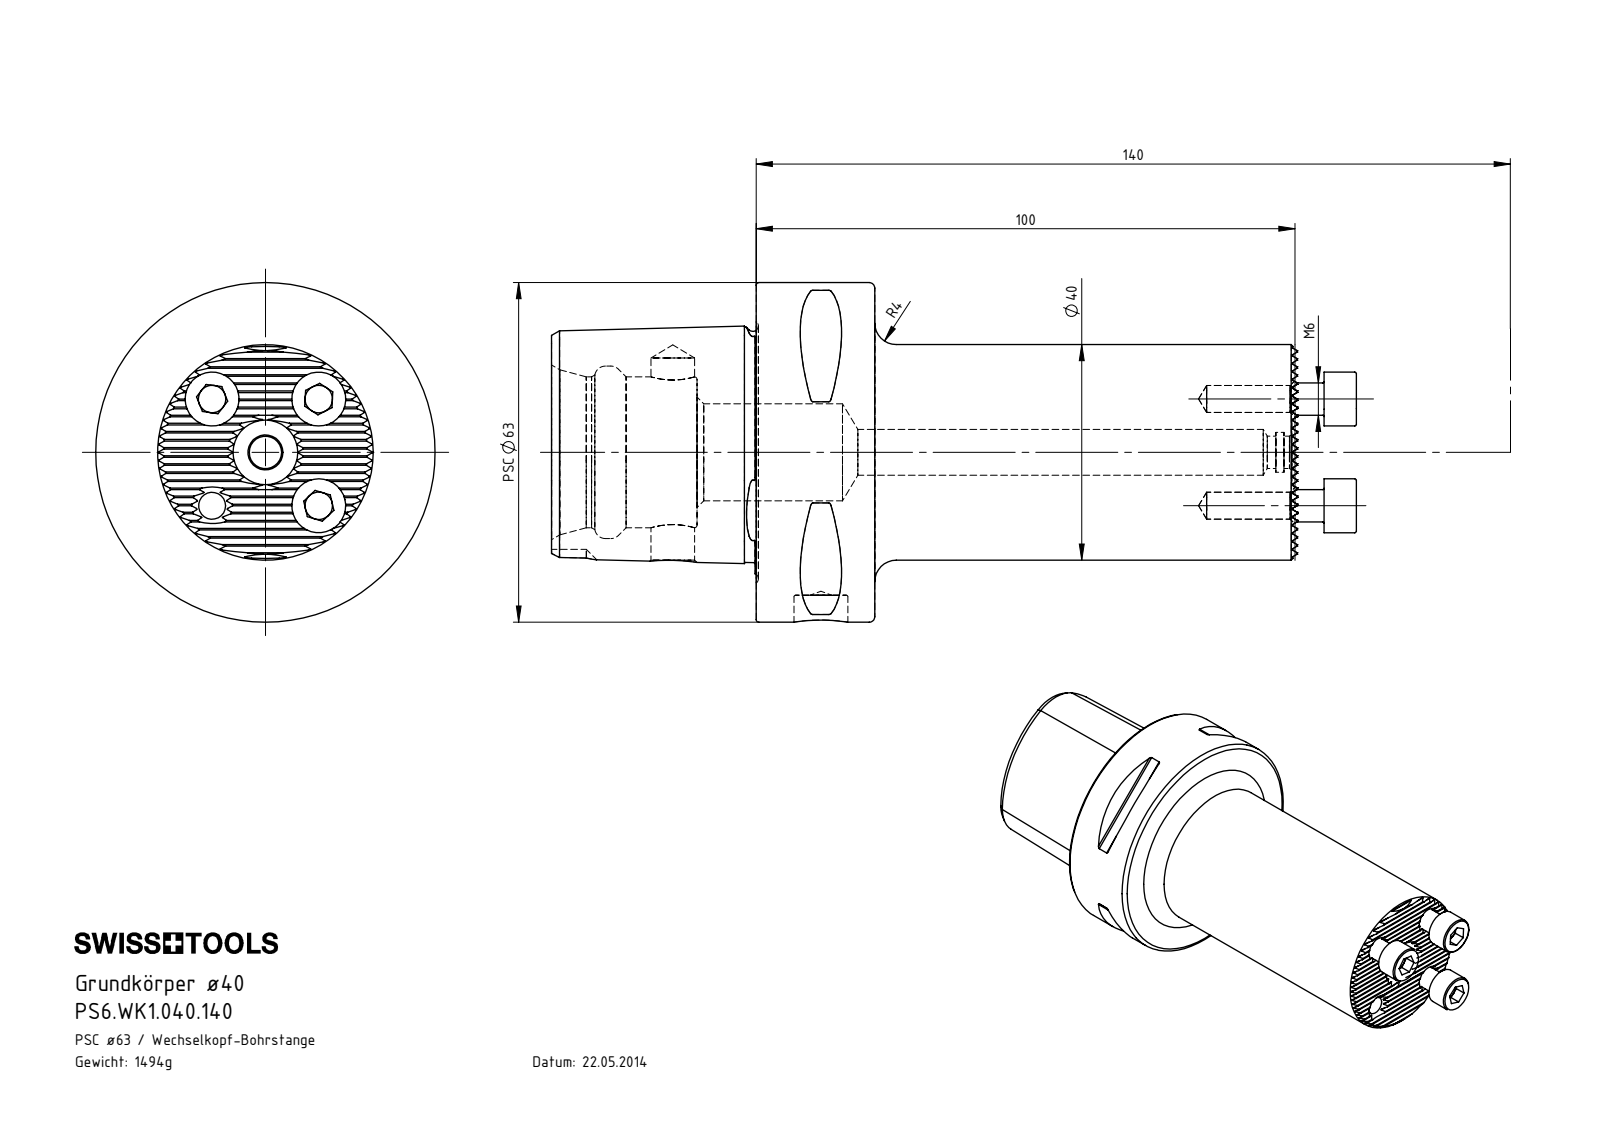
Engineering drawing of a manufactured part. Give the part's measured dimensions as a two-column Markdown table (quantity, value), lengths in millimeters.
| quantity | value |
| --- | --- |
| part name | PS6-WK1.040.140; DIN 3771 - 6x1; ISO 4762 - M6 x 16; PS6-WK1.040.140_A |
| STEP written by | SolidWorks 2012 (AUTOMOTIVE_DESIGN) |
| units | millimeters |
| bodies | 6 solids, 488 faces (242 planar, 111 cylindrical, 135 other) |
| overall size | 149.4 × 63 × 63 |
| volume | 191 514 mm³ |
| surface area | 36 011 mm² |
| round holes (diameter × count) | 5 × 4, 4 × 1, 6 × 1, 7.4 × 1, 8.1 × 1, 8.5 × 1, 18 × 1, 28 × 1, 32 × 1 |
| round bosses / shafts (diameter × count) | 10 × 4, 6 × 4, 63 × 1, 40 × 1 |
| partial cylindrical surfaces (radius × count) | 0.12 × 27, 0.5 × 8, 6 × 1 |
| main face-to-face distances | 22, 1.3, 2.6, 3.9, 11, 5.2, 12.99, 38, 60, 9.09 |
| hole center spacings | 14, 19.8, 28, 27.5 |
